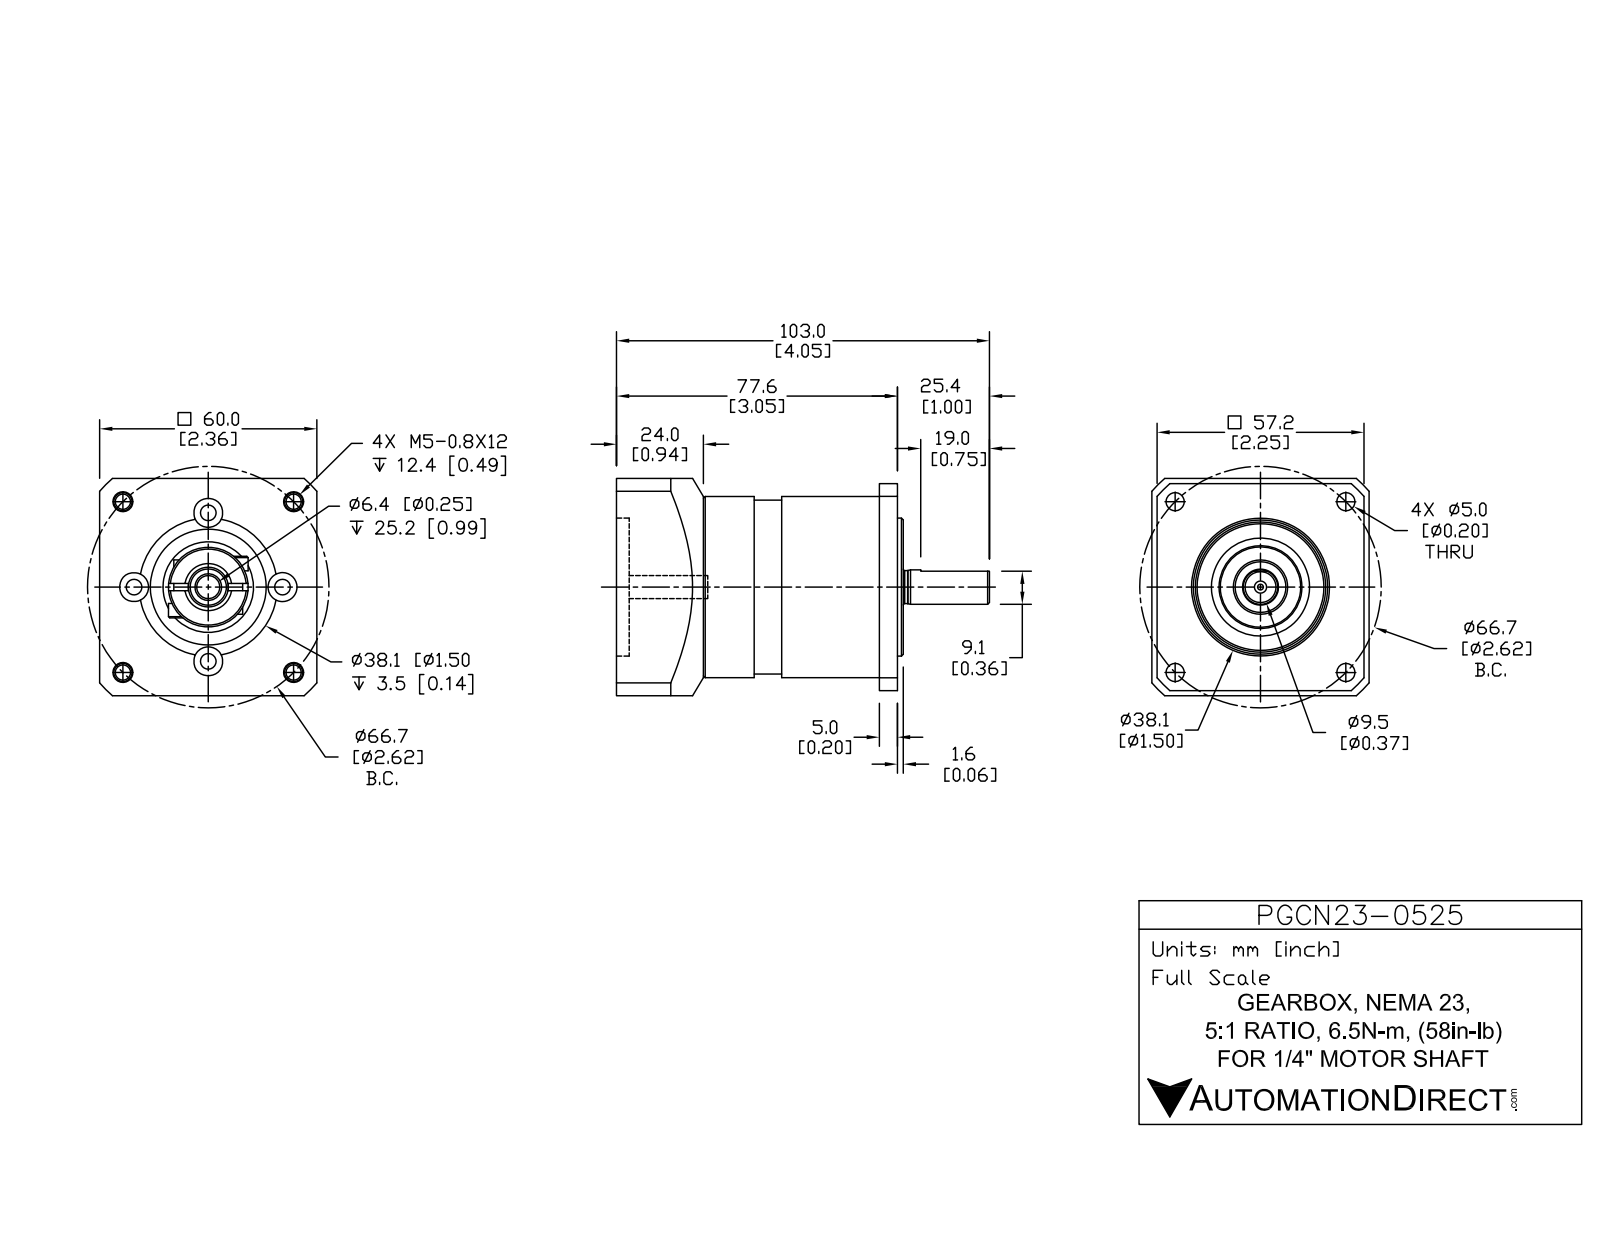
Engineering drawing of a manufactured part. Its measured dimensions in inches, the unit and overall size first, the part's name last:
Units: inches
Overall size (bounding box): 4.055 × 2.362 × 2.362
Round holes (diameter × count): ⌀0.165 ×4, ⌀0.169 ×4, ⌀0.197 ×4, ⌀0.315 ×4, ⌀0.157 ×2, ⌀0.354 ×2, ⌀0.063 ×1, ⌀0.25 ×1, ⌀0.433 ×1, ⌀0.984 ×1, ⌀1.067 ×1, ⌀1.26 ×1
Round bosses / shafts (diameter × count): ⌀0.276 ×2, ⌀1.969 ×1, ⌀1.89 ×1, ⌀0.902 ×1, ⌀0.874 ×1, ⌀0.866 ×1, ⌀0.591 ×1, ⌀0.375 ×1
Partial cylindrical surfaces — rounded edges, fillets, slot ends (radius × count): R0.157 ×2, R1.496 ×1, R1.575 ×1
Main face-to-face distances: 3.055, 2.362, 2.11, 0.945, 0.197, 1.913, 2.858, 0.118, 0.056, 2.306
Hole centre spacings: 0.936, 1.968, 0.807, 1.141, 1.312, 1.856, 0.051, 0.591
Volume: 10.46 in³ · Surface area: 55.99 in²
Bodies: 3 solids, 251 faces (69 planar, 114 cylindrical, 68 other)
Part name (STEP PRODUCT): PE-N23-I 11mm Input_1; PGCN23-0525; N23-F03_1; Bushing_.25x11x14.9_1
STEP written by: SolidWorks 2014 (AUTOMOTIVE_DESIGN)
